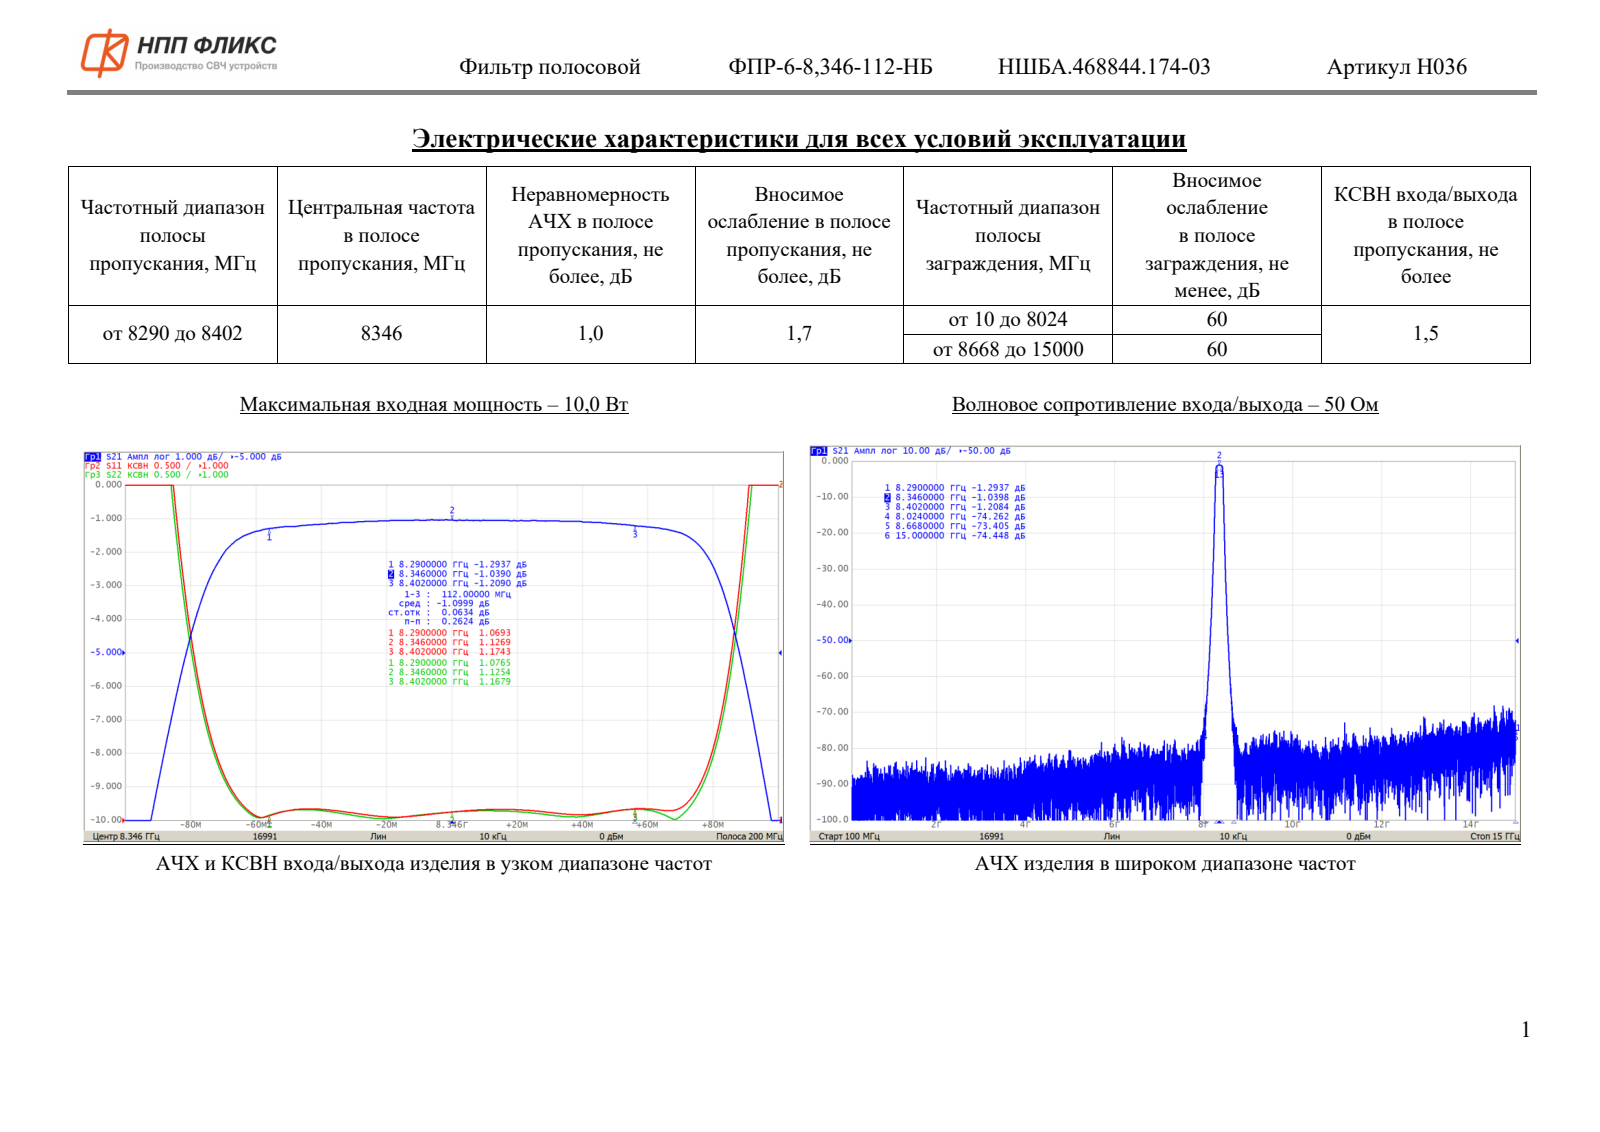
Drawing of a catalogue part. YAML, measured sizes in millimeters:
part_name: "НШБА.468844.174-03_Фильтр ФПР-6-8,346-112-НБ"
step_written_by: "ASCON Math Kernel (CONFIG_CONTROL_DESIGN)"
units: millimeters
bodies: {solids: 38, faces: 1281, planar: 859, cylindrical: 200, other: 222}
overall_size: [86, 21.5, 19.1]
volume: 25542
surface_area: 15156
round_holes:
  - {diameter: 2.7, count: 16}
  - {diameter: 5.2, count: 14}
  - {diameter: 1.6, count: 11}
  - {diameter: 2.5, count: 6}
  - {diameter: 2.9, count: 4}
  - {diameter: 2.6, count: 2}
  - {diameter: 0.95, count: 1}
  - {diameter: 1.15, count: 1}
  - {diameter: 4.21, count: 1}
  - {diameter: 4.61, count: 1}
round_bosses_or_shafts:
  - {diameter: 5, count: 16}
  - {diameter: 2.5, count: 16}
  - {diameter: 2, count: 11}
  - {diameter: 3.8, count: 6}
  - {diameter: 3.6, count: 6}
  - {diameter: 3, count: 6}
  - {diameter: 2.6, count: 6}
  - {diameter: 6.2, count: 1}
partial_cylinders:
  - {radius: 2.5, count: 4}
  - {radius: 3, count: 4}
  - {radius: 0.5, count: 3}
  - {radius: 0.25, count: 1}
  - {radius: 0.75, count: 1}
  - {radius: 0.88, count: 1}
face_to_face_distances: [15.5, 19, 3, 18.5, 1.5, 0.5, 19.1, 16.5, 2, 1]
hole_center_spacings: [8.6, 10, 12.21, 16.55, 20, 21.19, 25.96, 30]
